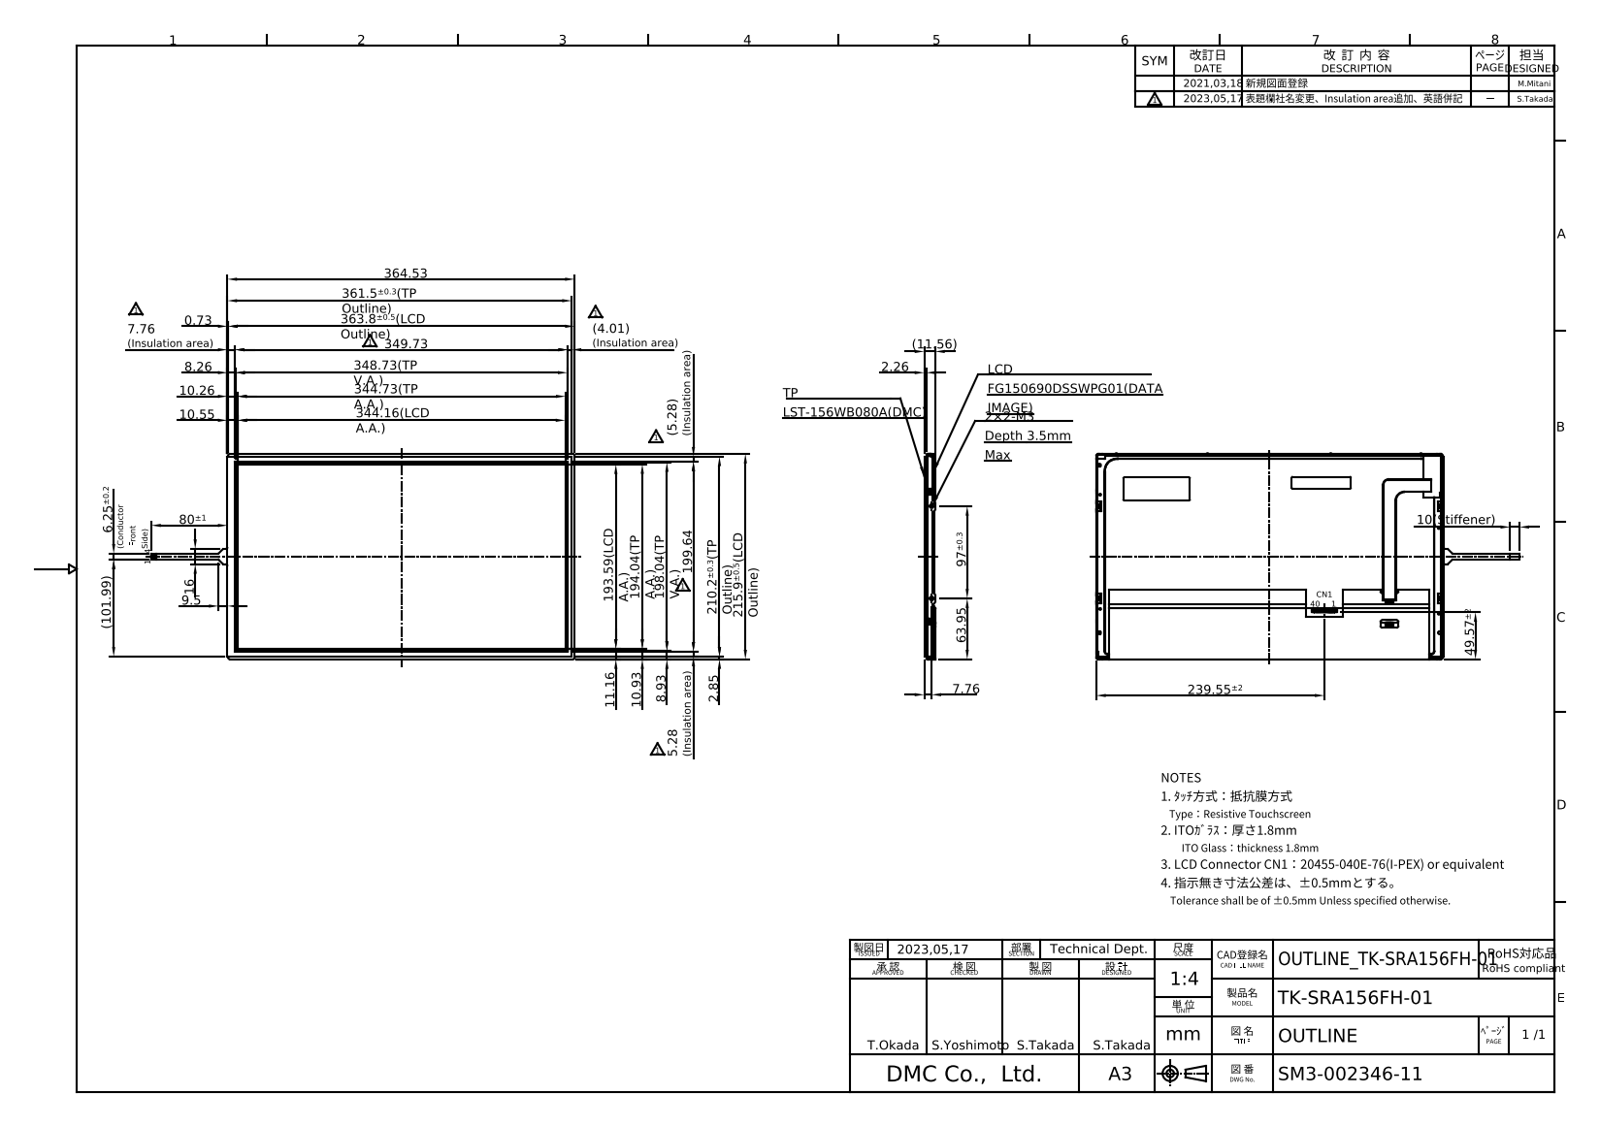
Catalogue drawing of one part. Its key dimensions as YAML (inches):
part_name: "HP_TK-SRA156FH-01"
step_written_by: "Autodesk Inventor 2020 (AUTOMOTIVE_DESIGN)"
units: inches
bodies: {solids: 1, faces: 4618, planar: 2798, cylindrical: 1492, other: 328}
overall_size: [17.501, 8.504, 0.455]
volume: 16.18
surface_area: 822.2
round_holes:
  - {diameter: 0.035, count: 4}
  - {diameter: 0.12, count: 4}
  - {diameter: 0.177, count: 3}
  - {diameter: 0.02, count: 2}
  - {diameter: 0.102, count: 2}
  - {diameter: 0.157, count: 2}
round_bosses_or_shafts:
  - {diameter: 0.098, count: 4}
  - {diameter: 0.165, count: 2}
partial_cylinders:
  - {radius: 0.02, count: 121}
  - {radius: 0.039, count: 120}
  - {radius: 0.004, count: 98}
  - {radius: 0.012, count: 96}
  - {radius: 0.008, count: 63}
  - {radius: 0.031, count: 44}
  - {radius: 0.024, count: 31}
  - {radius: 0.028, count: 20}
face_to_face_distances: [0.083, 0.141, 0.058, 0.05, 0.132, 0.331, 0.199, 0.19, 0.248, 0.031]
hole_center_spacings: [6.929, 14.055, 15.67, 0.788, 0.802, 0.985, 0.998, 1.187]
